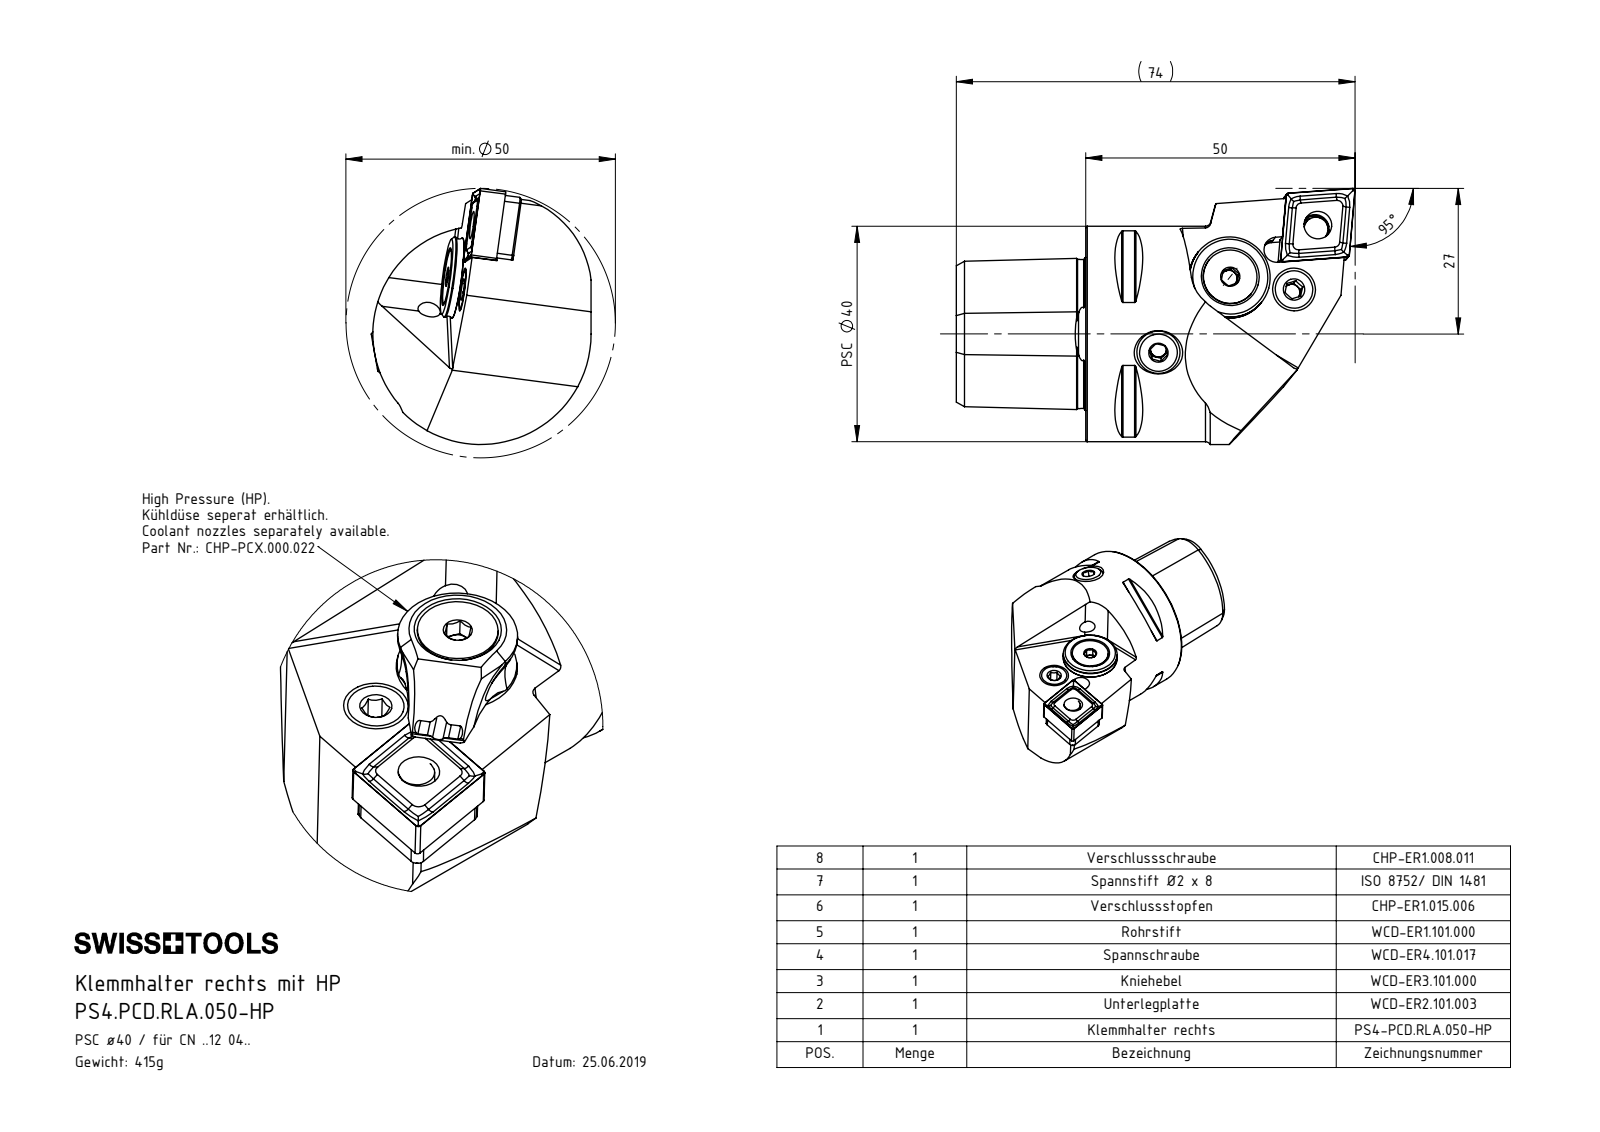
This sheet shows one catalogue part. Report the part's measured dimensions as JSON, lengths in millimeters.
{"part_name": "DIN 3771 - 13x1; WCD-ER3.101.000_A; CHP-ER1.015.006_A; CNMG120404 (+8 more)", "step_written_by": "SolidWorks 2017 (AUTOMOTIVE_DESIGN)", "units": "millimeters", "bodies": {"solids": 11, "faces": 460, "planar": 134, "cylindrical": 116, "other": 210}, "overall_size": [74, 47.5, 40.8], "volume_mm3": 52401, "surface_area_mm2": 17601, "round_holes": [[4.2, 3], [7, 2], [1.2, 1], [2, 1], [2.5, 1], [3, 1], [4, 1], [4.6, 1], [5, 1], [5.16, 1], [5.2, 1], [6.4, 1]], "round_bosses_or_shafts": [[8, 2], [40, 1], [15, 1], [13.4, 1], [10, 1], [7.9, 1], [6.4, 1], [5.5, 1]], "partial_cylinders_radius": [[0.3, 8], [0.4, 4], [1, 4], [0.5, 2], [2.5, 2], [2.1, 1], [2.2, 1], [2.35, 1]], "face_to_face_distances": [4.5, 4.45, 24, 3.13, 3.18, 7.63, 0.31, 15.52, 12.7, 11.8], "hole_center_spacings": [4.51, 4.5, 4.53, 12.27, 12.29, 12.59, 12.6, 12.8]}
